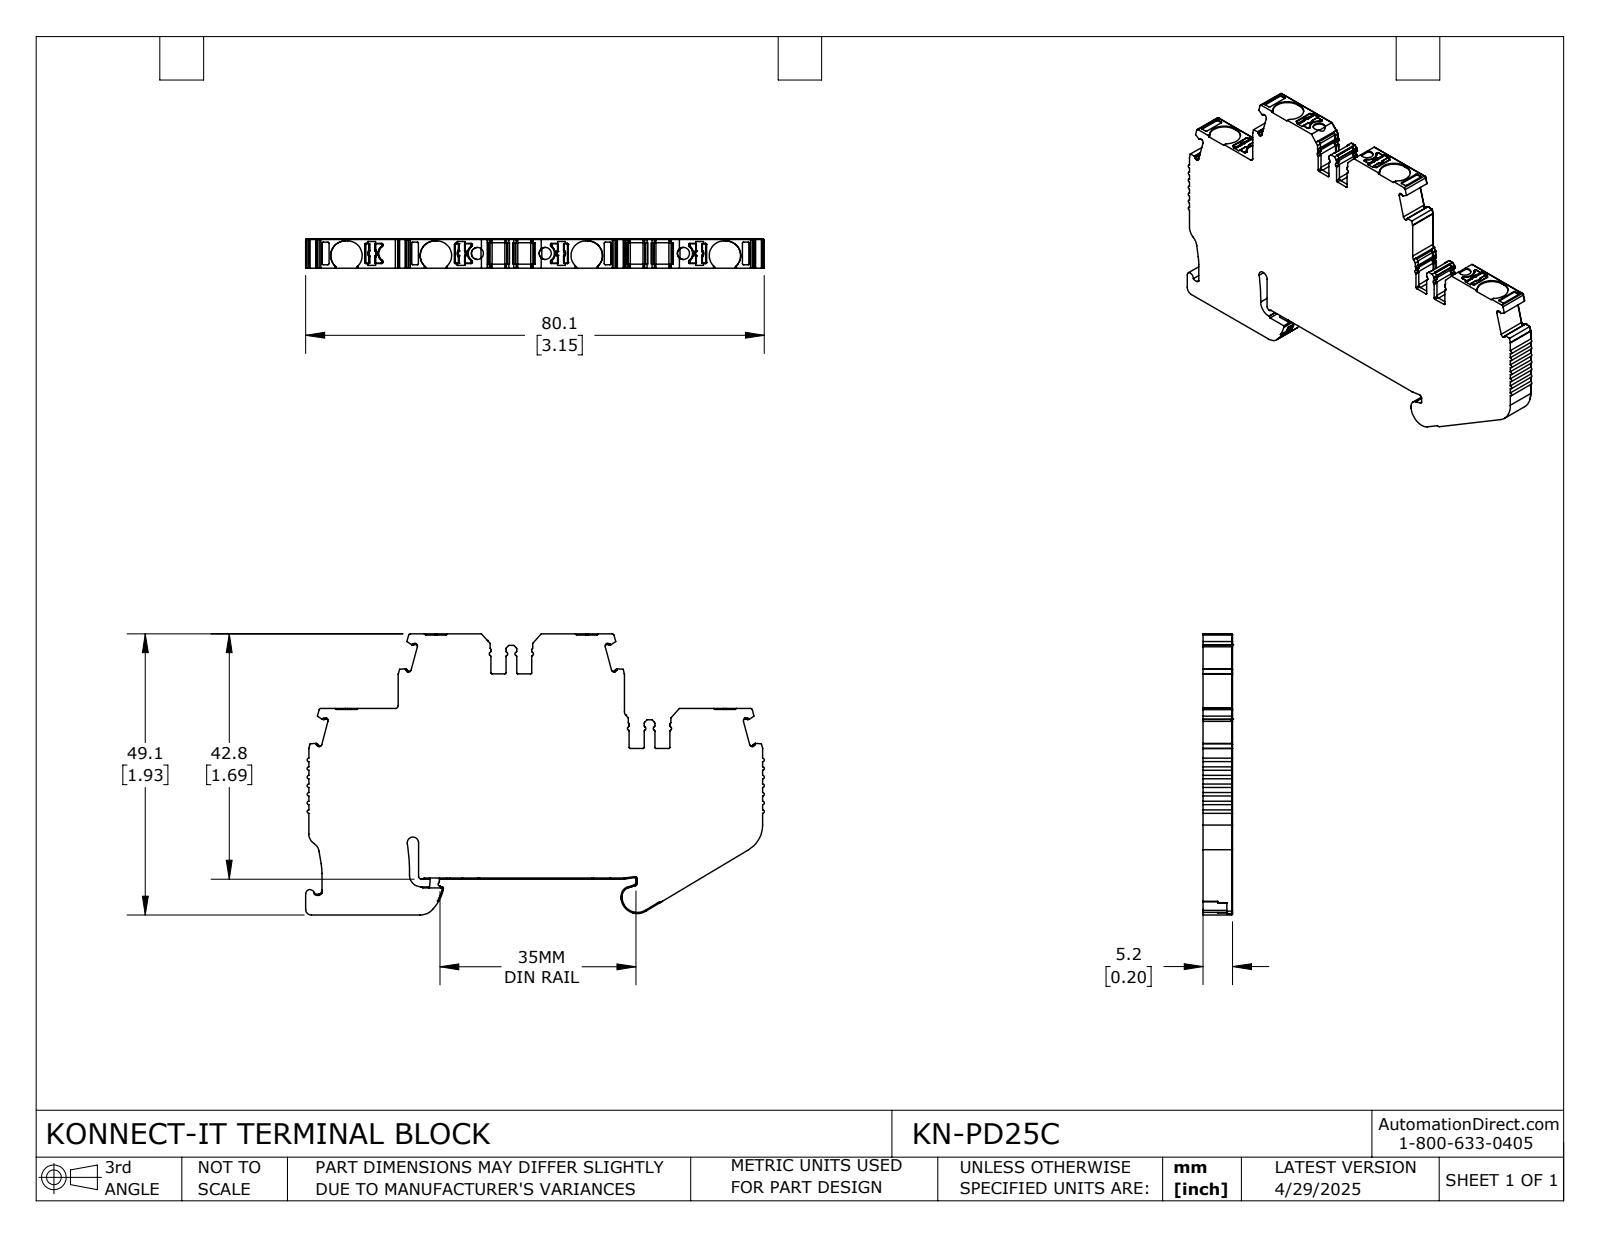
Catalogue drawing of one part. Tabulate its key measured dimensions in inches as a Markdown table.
| quantity | value |
| --- | --- |
| part name | KN-PD25C |
| STEP written by | SolidWorks 2024 (CONFIG_CONTROL_DESIGN) |
| units | inches |
| bodies | 1 solid, 1035 faces (503 planar, 463 cylindrical, 69 other) |
| overall size | 3.153 × 1.933 × 0.203 |
| volume | 0.886 in³ |
| surface area | 11.71 in² |
| round holes (diameter × count) | 0.083 × 3 |
| partial cylindrical surfaces (radius × count) | 0.008 × 99, 0.012 × 59, 0.004 × 41, 0.016 × 25, 0.02 × 20, 0.006 × 16, 0.024 × 9, 0.039 × 9 |
| main face-to-face distances | 0.203, 0.512, 1.166, 1.678, 0.246, 1.924, 0.95, 1.412, 0.504, 0.254 |
| hole center spacings | 0.466, 0.95, 1.417 |
